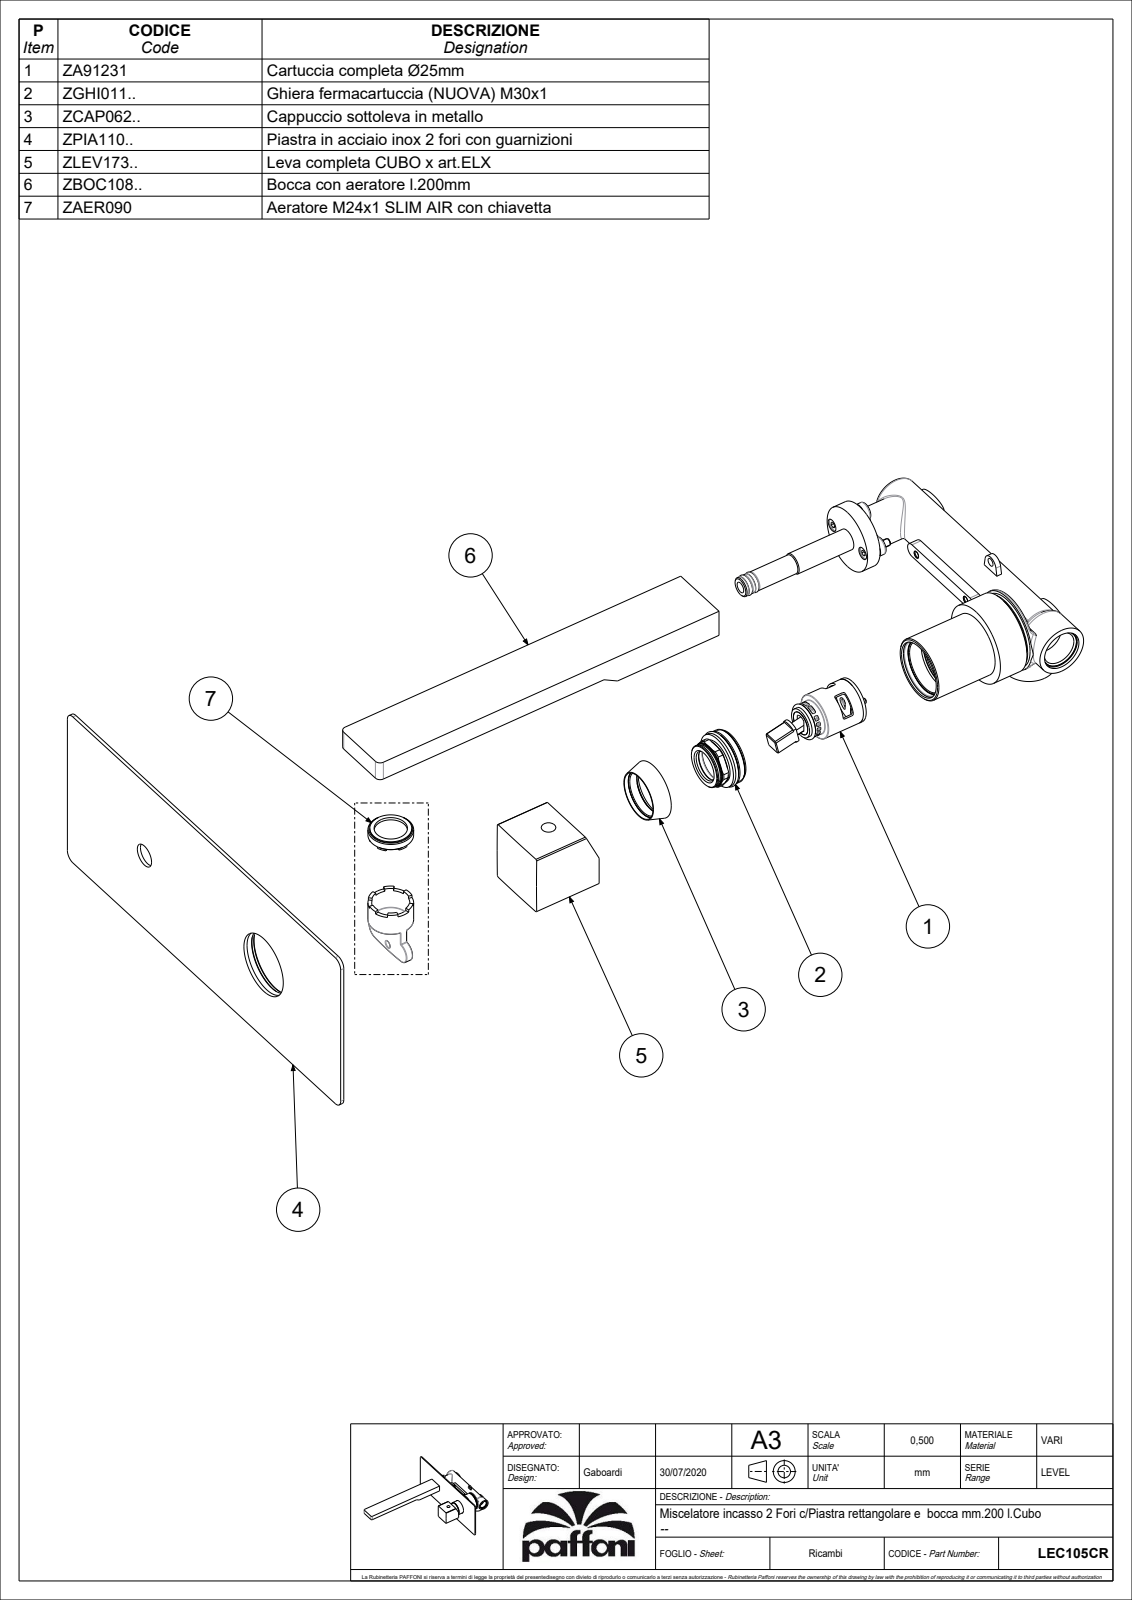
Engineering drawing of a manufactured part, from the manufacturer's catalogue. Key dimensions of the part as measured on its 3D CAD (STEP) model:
Part name (STEP PRODUCT): LEC105CR
STEP written by: CREO PARAMETRIC BY PTC INC, 2020044 (CONFIG_CONTROL_DESIGN)
Units: millimetres
Bodies: 2 solids, 713 faces (233 planar, 261 cylindrical, 219 other)
Overall size (bounding box): 250 × 220 × 100
Volume: 178 429 mm³ · Surface area: 105 764 mm²
Round holes (diameter × count): ⌀6 ×2, ⌀11 ×2, ⌀3 ×1, ⌀4.2 ×1, ⌀5.5 ×1, ⌀12 ×1, ⌀13 ×1, ⌀15 ×1, ⌀16.7 ×1, ⌀17 ×1, ⌀17.5 ×1, ⌀19.2 ×1
Round bosses / shafts (diameter × count): ⌀35.2 ×1, ⌀30 ×1, ⌀27.7 ×1, ⌀25 ×1, ⌀23.8 ×1, ⌀22.5 ×1, ⌀19 ×1, ⌀18.5 ×1
Partial cylindrical surfaces — rounded edges, fillets, slot ends (radius × count): R0.5 ×56, R1 ×7, R2 ×4, R5 ×4, R2.1 ×2, R2.5 ×2, R3 ×2, R3.5 ×2
Main face-to-face distances: 2, 11.5, 35, 9.75, 26.25, 36, 5, 16.5, 14.75, 73.5
Hole centre spacings: 109, 195.64
